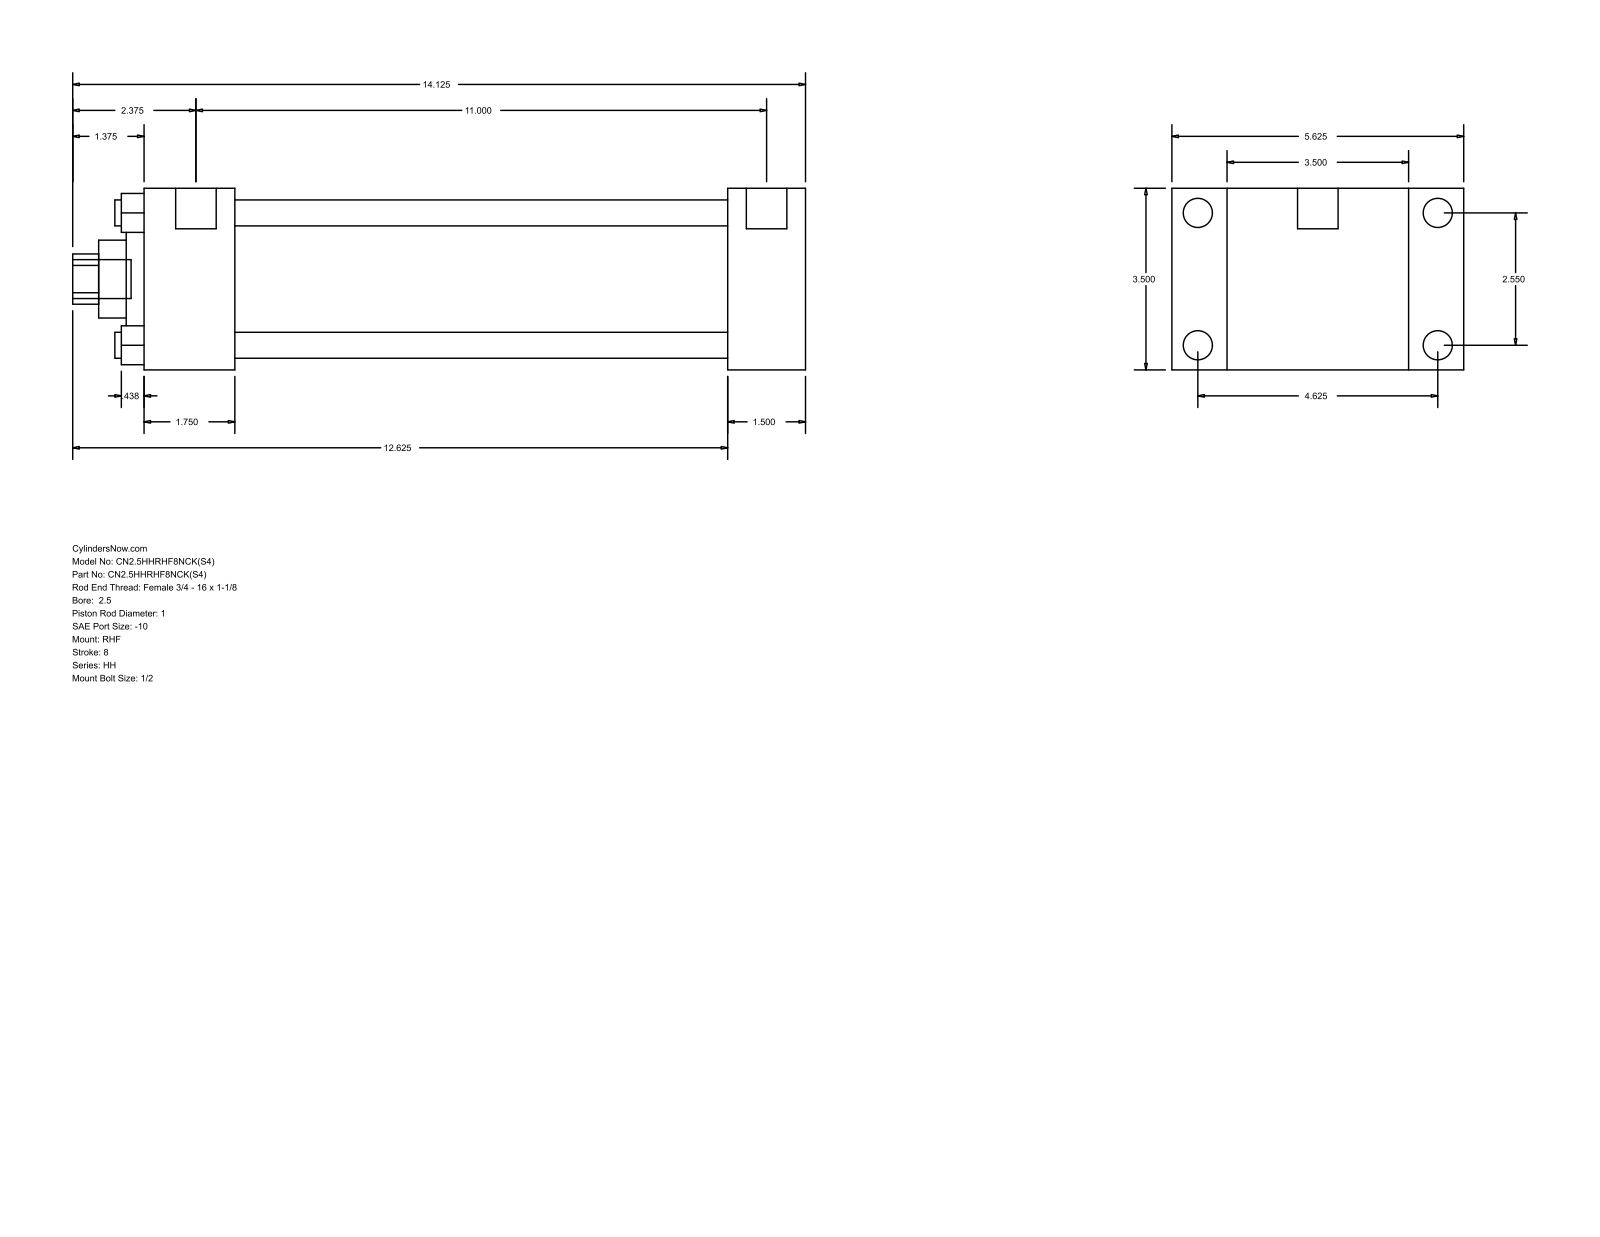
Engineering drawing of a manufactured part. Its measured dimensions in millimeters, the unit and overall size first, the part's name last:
Units: millimetres
Overall size (bounding box): 358.77 × 142.88 × 88.9
Round holes (diameter × count): ⌀12.7 ×4, ⌀25.4 ×1, ⌀38.1 ×1, ⌀60.33 ×1, ⌀73.03 ×1
Round bosses / shafts (diameter × count): ⌀14.3 ×4, ⌀5.56 ×4, ⌀19.84 ×2, ⌀19.05 ×1
Partial cylindrical surfaces — rounded edges, fillets, slot ends (radius × count): R12.29 ×1
Main face-to-face distances: 88.9, 38.09, 26.99, 115.89, 285.76, 323.85, 142.88, 44.46, 241.3, 279.39
Hole centre spacings: 45.79, 64.76, 91.58
Bodies: 0 solids, 90 faces (61 planar, 29 cylindrical, 0 other)
Part name (STEP PRODUCT): HH_RHF__0250_1
STEP written by: GSSL Pune (CONFIG_CONTROL_DESIGN)
